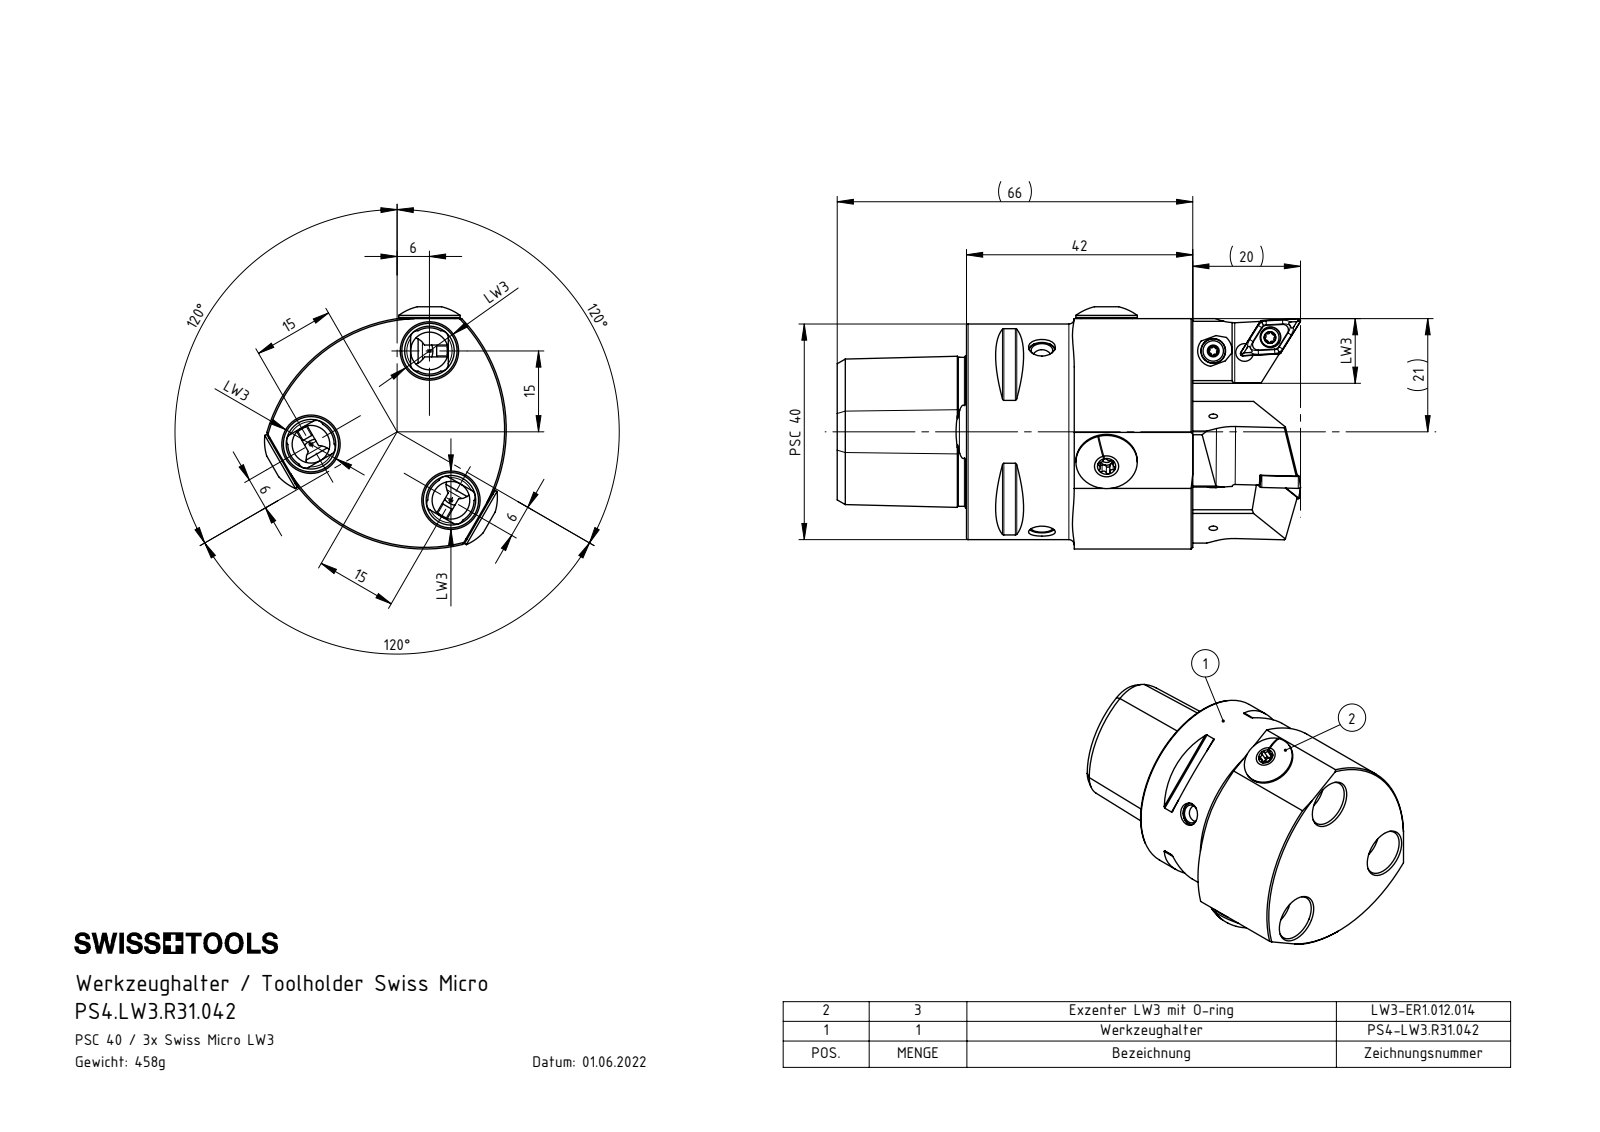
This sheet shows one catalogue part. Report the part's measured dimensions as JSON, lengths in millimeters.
{"part_name": "PS4-LW3.R31.042_B; PS4.LW3.R31.042; LW3-ER1.012.014; LW3-ER1.012.014_E_Standard<Wie bearbeitet> (+2 more)", "step_written_by": "SolidWorks 2022 (AUTOMOTIVE_DESIGN)", "units": "millimeters", "bodies": {"solids": 13, "faces": 458, "planar": 161, "cylindrical": 156, "other": 141}, "overall_size": [66, 44.94, 44.87], "volume_mm3": 58182, "surface_area_mm2": 18817, "round_holes": [[4.2, 6], [1, 3], [2.4, 3], [5.5, 3], [7, 3], [9.21, 3], [4.6, 1], [10, 1], [12.5, 1], [18, 1], [20, 1]], "round_bosses_or_shafts": [[11.4, 3], [9.5, 3], [7.7, 3], [5, 3], [40, 1]], "partial_cylinders_radius": [[0.34, 18], [0.59, 18], [1.3, 12], [0.3, 8], [2.5, 6], [3.6, 3], [3.7, 3], [3.75, 3]], "face_to_face_distances": [42, 1.1, 11.6, 24, 66, 10.2, 9.1, 2, 15.52, 1.5], "hole_center_spacings": [16.16, 27.98, 16.15, 23.5, 27.99]}
